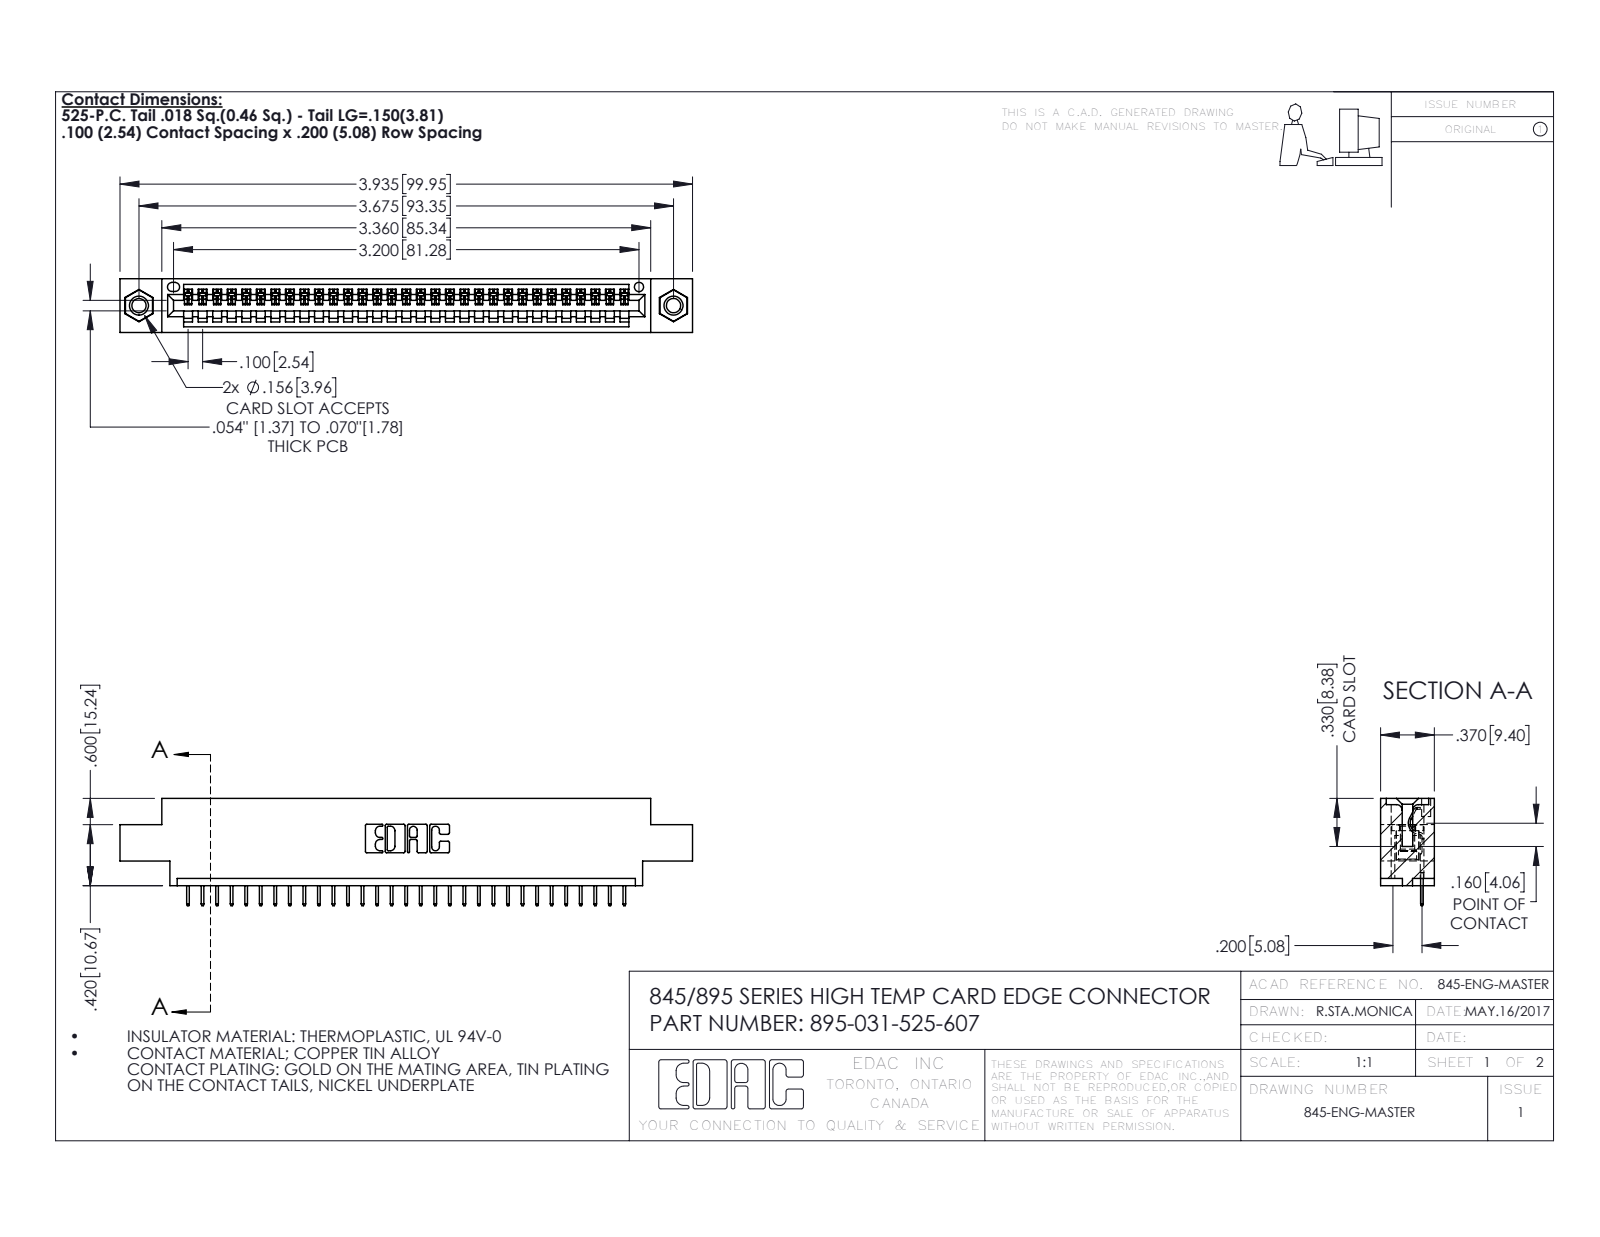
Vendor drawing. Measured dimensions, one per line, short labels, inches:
name: 345-292-001_345-293-125; 895-031-525-607; 845 Part_0.170 Offset - 0.156 Dia-TI; 345-250-001_345-250-005-103
written by: SolidWorks 2020 (CONFIG_CONTROL_DESIGN)
unit: in
bodies: 34 solids, 2112 faces (1542 planar, 554 cylindrical, 16 other)
size: 3.935 × 0.737 × 0.37
volume: 0.558 in³; area: 18.21 in²
holes: 2× ⌀0.098, 2× ⌀0.125, 2× ⌀0.156, 1× ⌀0.064
bosses: 2× ⌀0.155
rounds: 62× R0.006, 22× R0.01, 6× R0.007, 6× R0.031, 3× R0.026, 2× R0.031, 2× R0.04, 1× R0.014
face distances: 0.072, 0.298, 0.37, 0.2, 0.098, 0.272, 0.025, 0.225, 0.175, 0.072
hole spacings: 0.27, 3.44, 3.675
